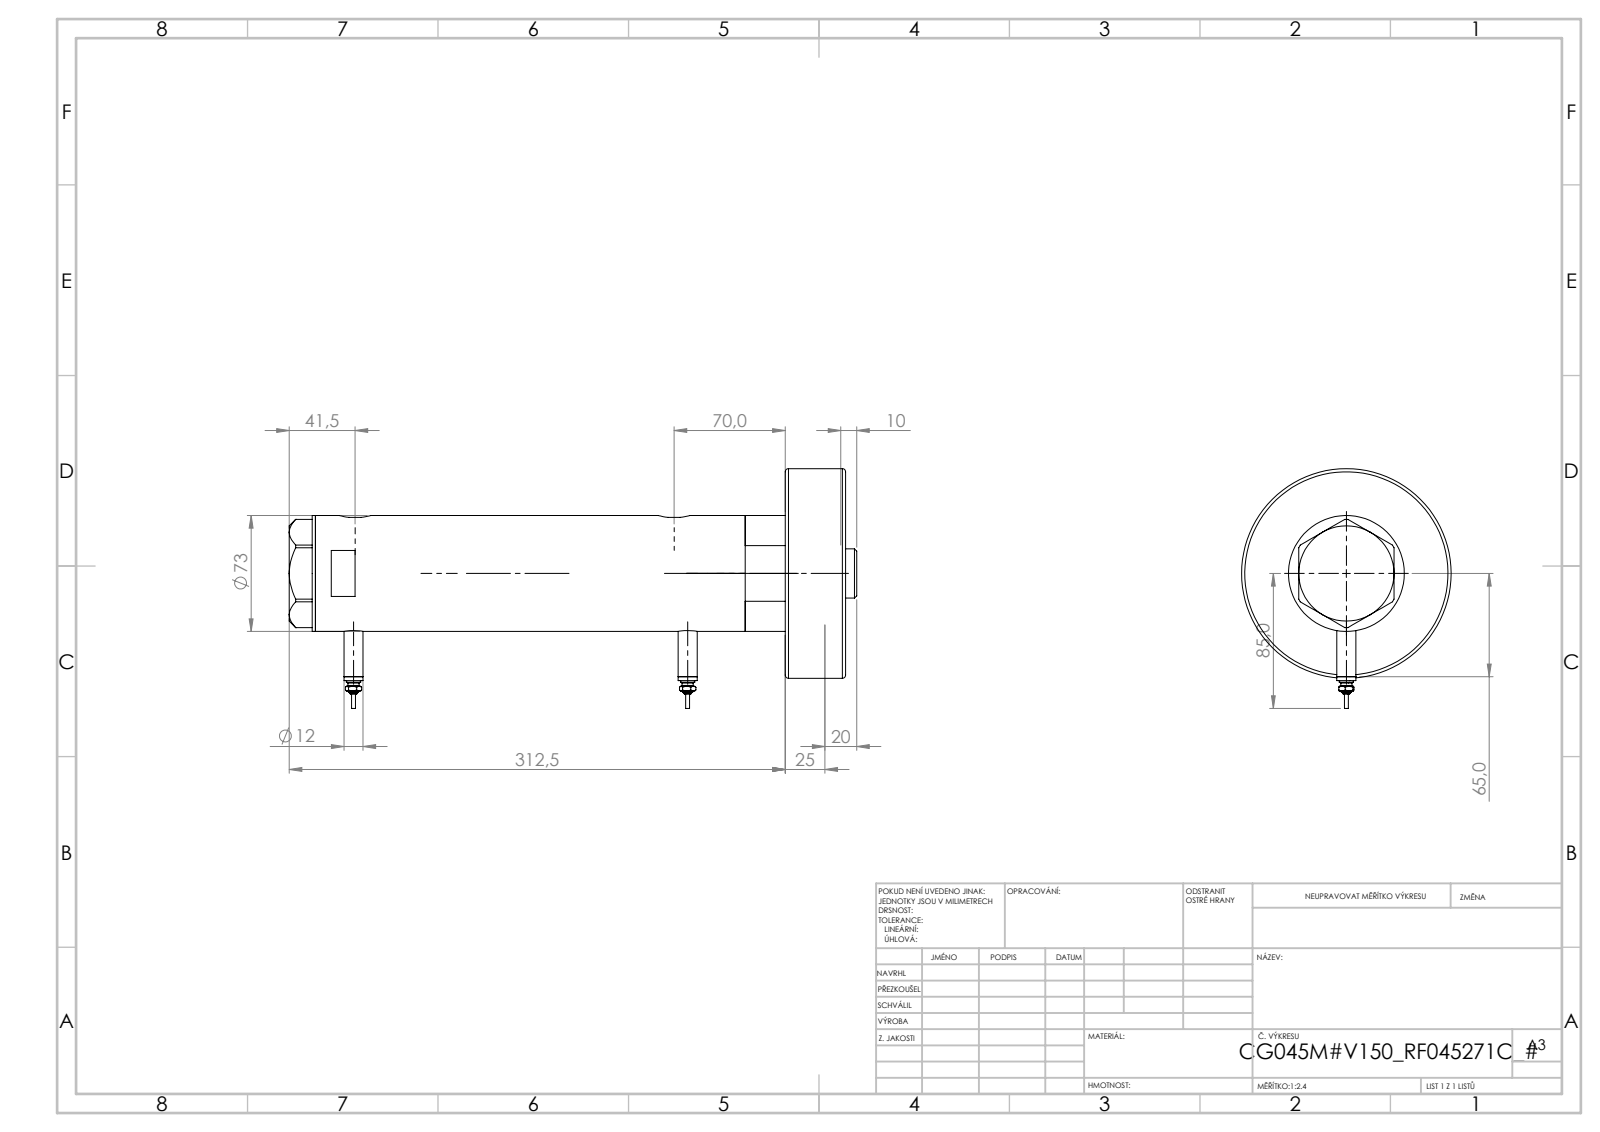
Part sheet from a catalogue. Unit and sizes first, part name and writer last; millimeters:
Units: millimetres
Overall size (bounding box): 357.5 × 151 × 132
Round holes (diameter × count): ⌀12.5 ×2, ⌀13.16 ×2, ⌀10.5 ×1, ⌀32 ×1, ⌀33.5 ×1, ⌀45 ×1, ⌀48 ×1, ⌀60 ×1, ⌀64 ×1
Round bosses / shafts (diameter × count): ⌀12 ×2, ⌀9 ×2, ⌀7 ×2, ⌀4.5 ×2, ⌀2.5 ×2, ⌀132 ×1, ⌀73 ×1, ⌀58 ×1
Partial cylindrical surfaces — rounded edges, fillets, slot ends (radius × count): R10 ×2
Main face-to-face distances: 38, 296, 334, 226, 70, 108, 26, 200, 270, 308
Hole centre spacings: 1, 8.5, 201, 202, 209.5, 210.5
Volume: 1 665 000 mm³ · Surface area: 245 334 mm²
Bodies: 7 solids, 222 faces (79 planar, 75 cylindrical, 68 other)
Part name (STEP PRODUCT): V270CG_VC; V270CG_FRONT; V270CG_271C; V270CG_BACK (+2 more)
STEP written by: SolidWorks 2019 (CONFIG_CONTROL_DESIGN)
